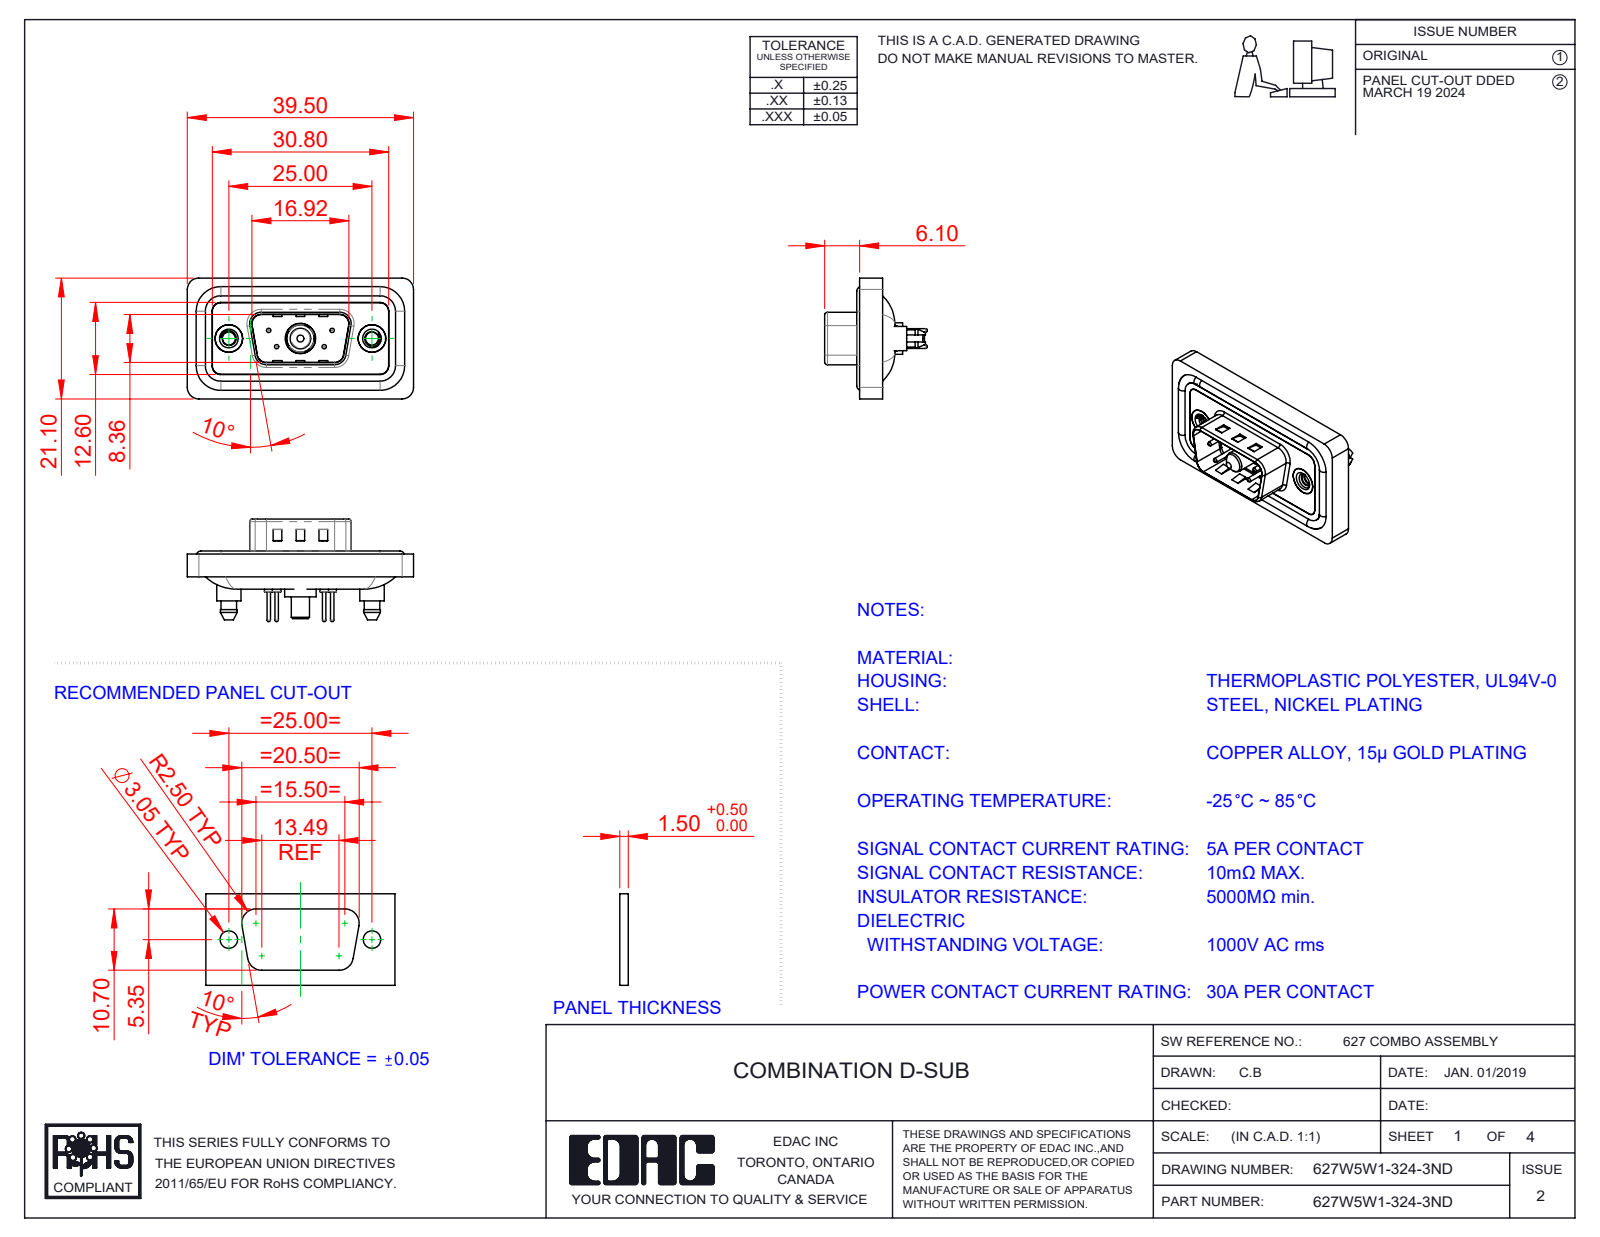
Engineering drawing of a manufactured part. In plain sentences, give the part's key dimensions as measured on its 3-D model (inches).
The part is named "627Combo Threaded Boardlock_5; 627W5W1-324-3ND; 627Combo Waterproof Housing_09 Contacts; 627Combo Contact Row 2_24 (+6 more)". Its 3-D file was written by "SolidWorks 2023 (CONFIG_CONTROL_DESIGN)". It is 13 solids with 656 faces: 199 planar, 295 cylindrical and 162 other. Overall it measures 1.555 by 0.831 by 0.705 inches. Its volume is 0.276 cubic inches and its surface area 11.29 square inches. Round holes: 4 of diameter 0.03, 4 of diameter 0.063, 4 of diameter 0.079, 2 of diameter 0.089, 2 of diameter 0.157, 2 of diameter 0.189, 2 of diameter 0.197, 1 of diameter 0.191, 1 of diameter 0.209. Round bosses or shafts: 4 of diameter 0.063, 4 of diameter 0.059, 4 of diameter 0.024, 2 of diameter 0.213, 2 of diameter 0.193, 2 of diameter 0.167, 1 of diameter 0.217, 1 of diameter 0.205. Partial cylindrical surfaces (rounded edges, fillets, slot ends): 24 of radius 0.059, 18 of radius 0.079, 10 of radius 0.063, 8 of radius 0.02, 4 of radius 0.01, 4 of radius 0.024, 4 of radius 0.026, 4 of radius 0.035. The main face-to-face distances are 0.016, 0.043, 0.114, 0.063, 0.059, 0.122, 0.02, 0.098, 0.157, 0.031. The hole center spacings are 0.124, 0.225, 0.28, 0.492, 0.713, 0.173, 0.173, 0.327.
